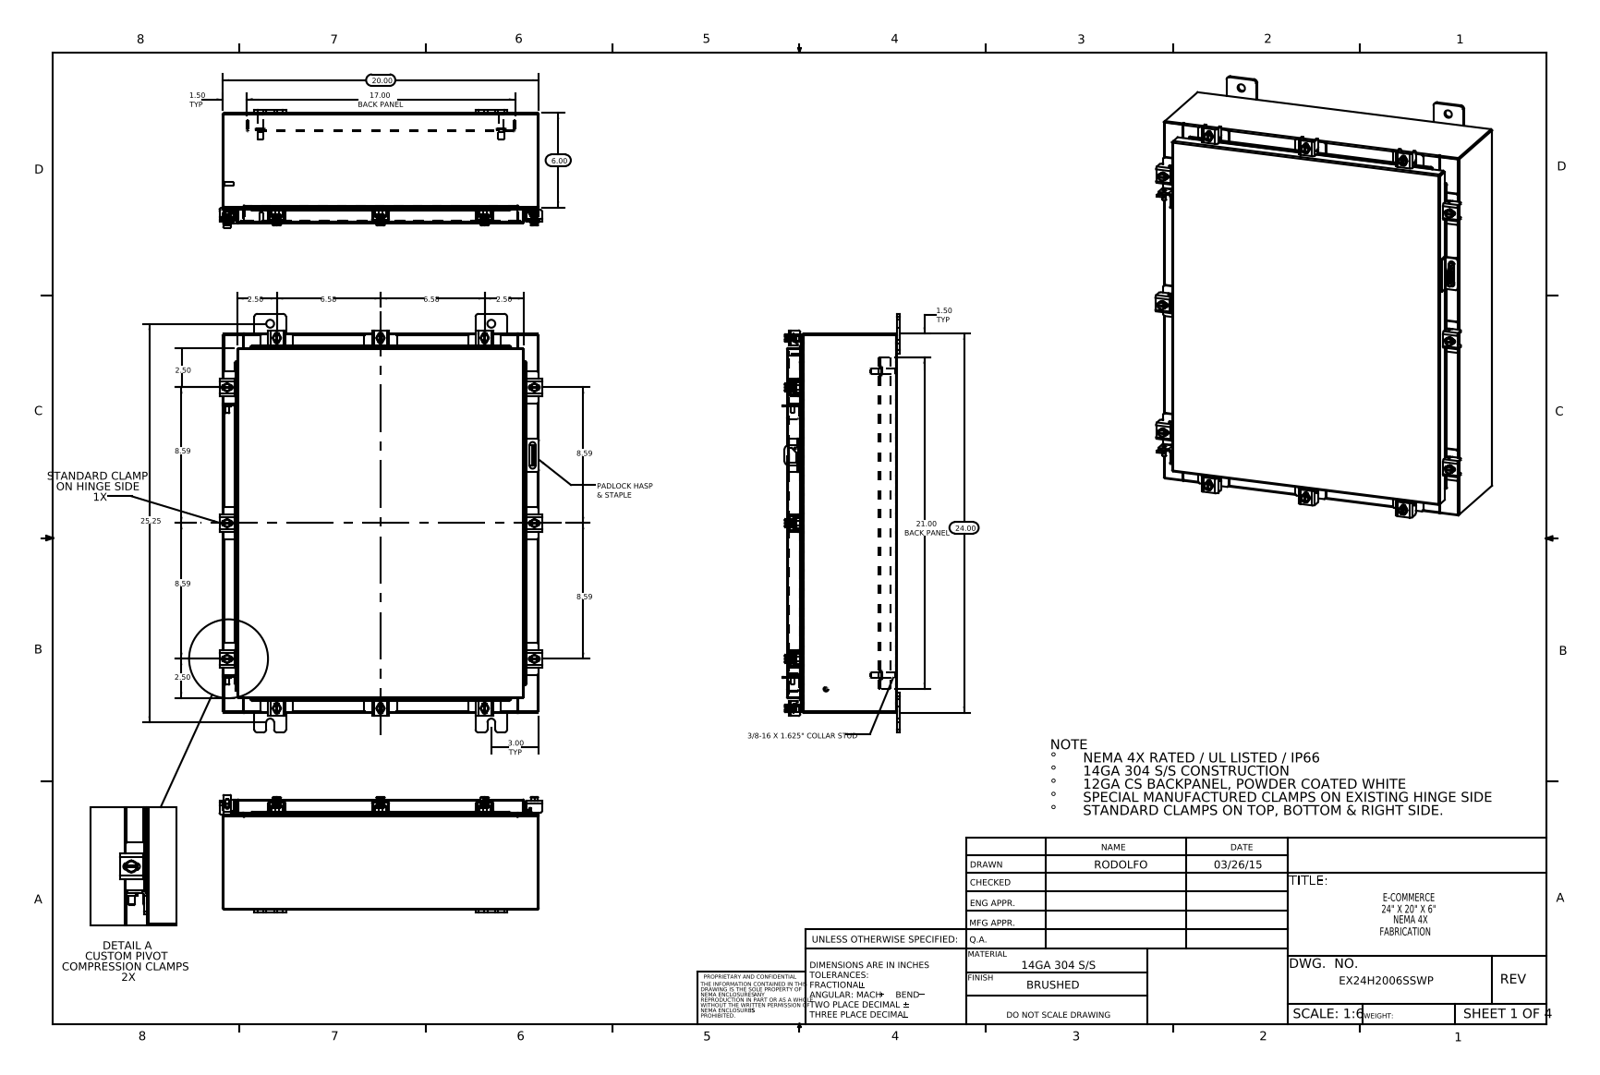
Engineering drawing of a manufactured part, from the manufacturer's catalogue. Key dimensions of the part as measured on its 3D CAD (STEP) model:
Part name (STEP PRODUCT): EX24H2006SSWP Standard Clamps; EX24H2006SSWP Backpanel; 22101002_RTP29; EX24H2006SSWP Special Clamp (+8 more)
STEP written by: SolidWorks 2014 (CONFIG_CONTROL_DESIGN)
Units: inches
Bodies: 81 solids, 2018 faces (1075 planar, 783 cylindrical, 160 other)
Overall size (bounding box): 26.5 × 20.421 × 7.453
Volume: 174.1 in³ · Surface area: 4 334 in²
Round holes (diameter × count): ⌀0.213 ×12, ⌀0.26 ×12, ⌀0.5 ×8, ⌀0.125 ×1, ⌀0.25 ×1
Round bosses / shafts (diameter × count): ⌀0.5 ×12, ⌀0.25 ×12, ⌀0.399 ×10, ⌀0.625 ×4, ⌀0.375 ×4, ⌀0.33 ×4, ⌀0.315 ×2, ⌀0.236 ×2
Partial cylindrical surfaces — rounded edges, fillets, slot ends (radius × count): R0.06 ×54, R0.013 ×24, R0.141 ×24, R0.19 ×24, R0.088 ×22, R0.12 ×22, R0.09 ×18, R0.05 ×17
Main face-to-face distances: 0.075, 6.9, 6.975, 6.826, 0.104, 1, 1.075, 5.826, 5.9, 1.179
Hole centre spacings: 2.347, 4.44, 8.594, 12.141, 16.602, 18.34, 20.082, 20.562
